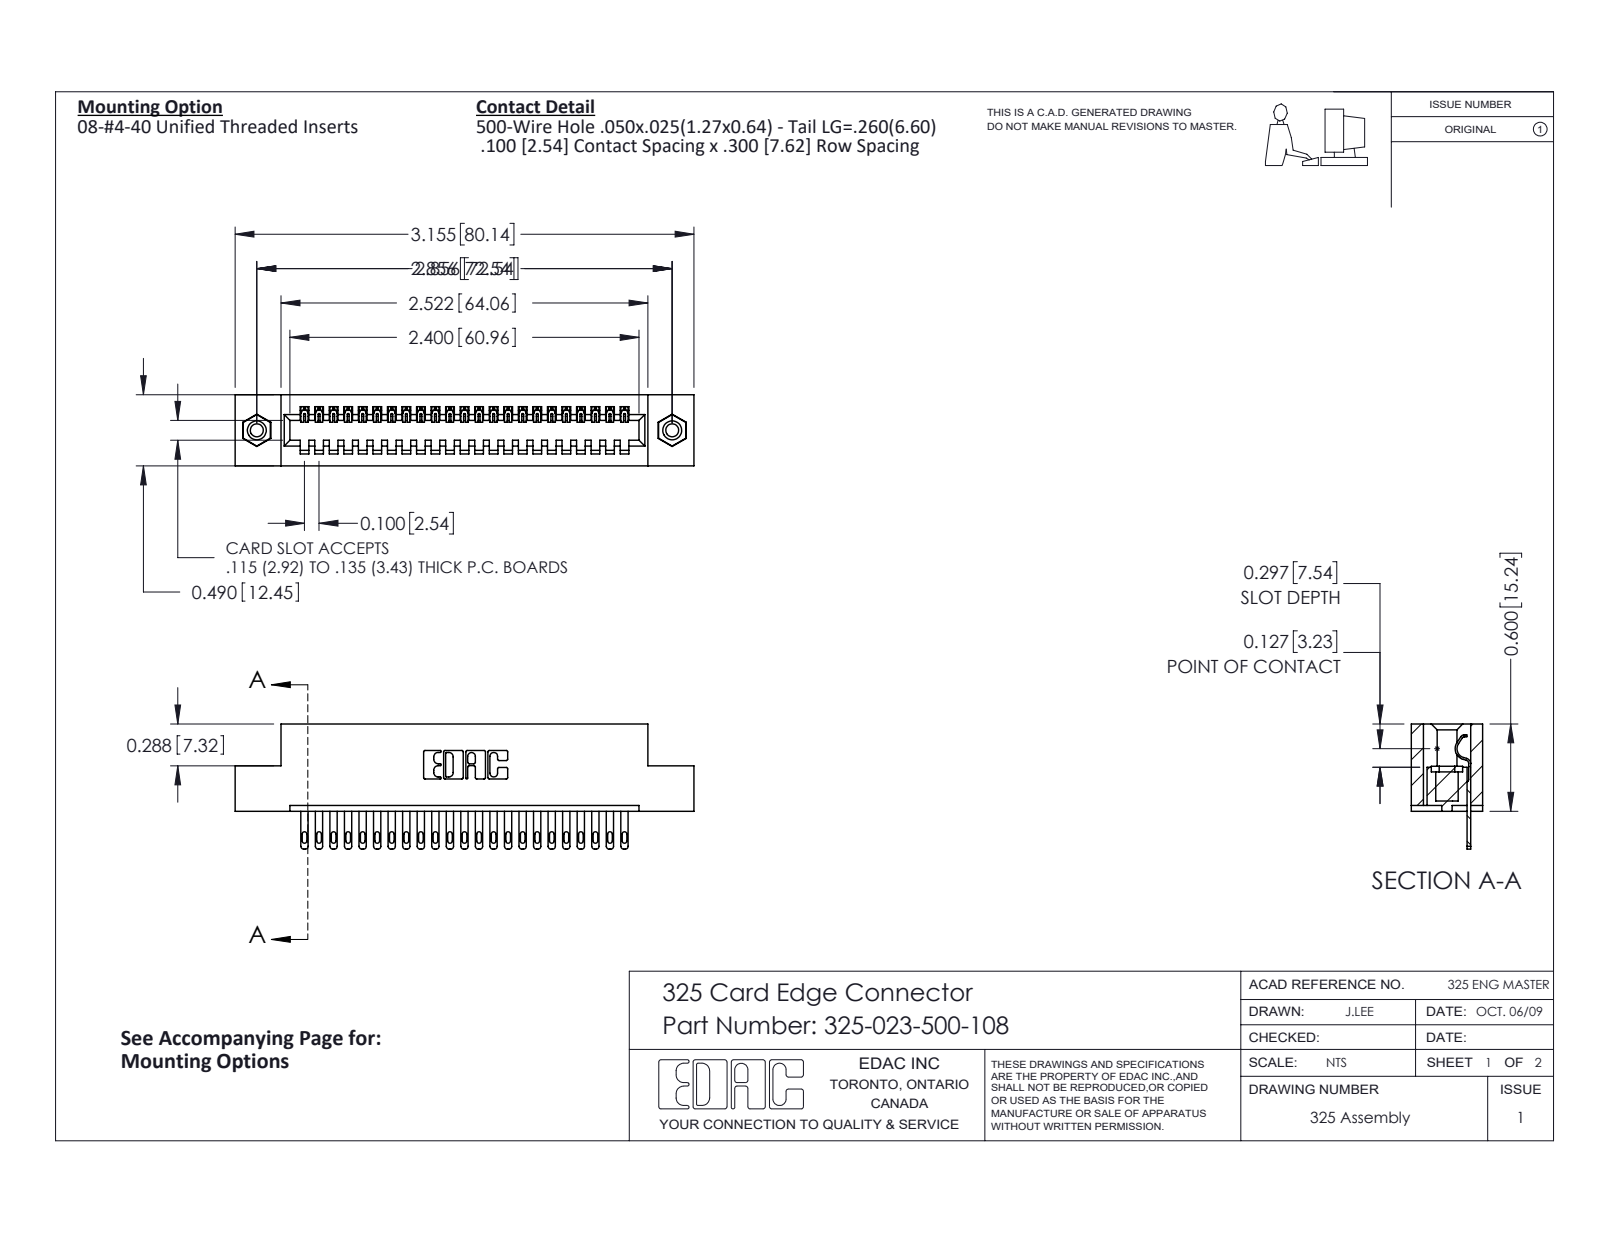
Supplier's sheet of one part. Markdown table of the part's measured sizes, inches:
| quantity | value |
| --- | --- |
| part name | 345-250-001_345-250-003-102; 325-292-001_325-293-100; 325 Part_TI; 325-023-500-108 |
| STEP written by | SolidWorks 2016 (CONFIG_CONTROL_DESIGN) |
| units | inches |
| bodies | 26 solids, 1416 faces (930 planar, 470 cylindrical, 16 other) |
| overall size | 3.155 × 0.86 × 0.49 |
| volume | 0.612 in³ |
| surface area | 16.6 in² |
| round holes (diameter × count) | 0.089 × 2, 0.125 × 2, 0.16 × 2 |
| round bosses / shafts (diameter × count) | 0.155 × 2 |
| partial cylindrical surfaces (radius × count) | 0.006 × 46, 0.016 × 46, 0.02 × 46, 0.01 × 22, 0.007 × 6, 0.031 × 6, 0.026 × 3, 0.014 × 1 |
| main face-to-face distances | 0.083, 0.407, 0.3, 0.49, 0.107, 0.383, 0.025, 0.04, 0.325, 0.6 |
| hole center spacings | 2.856 |
